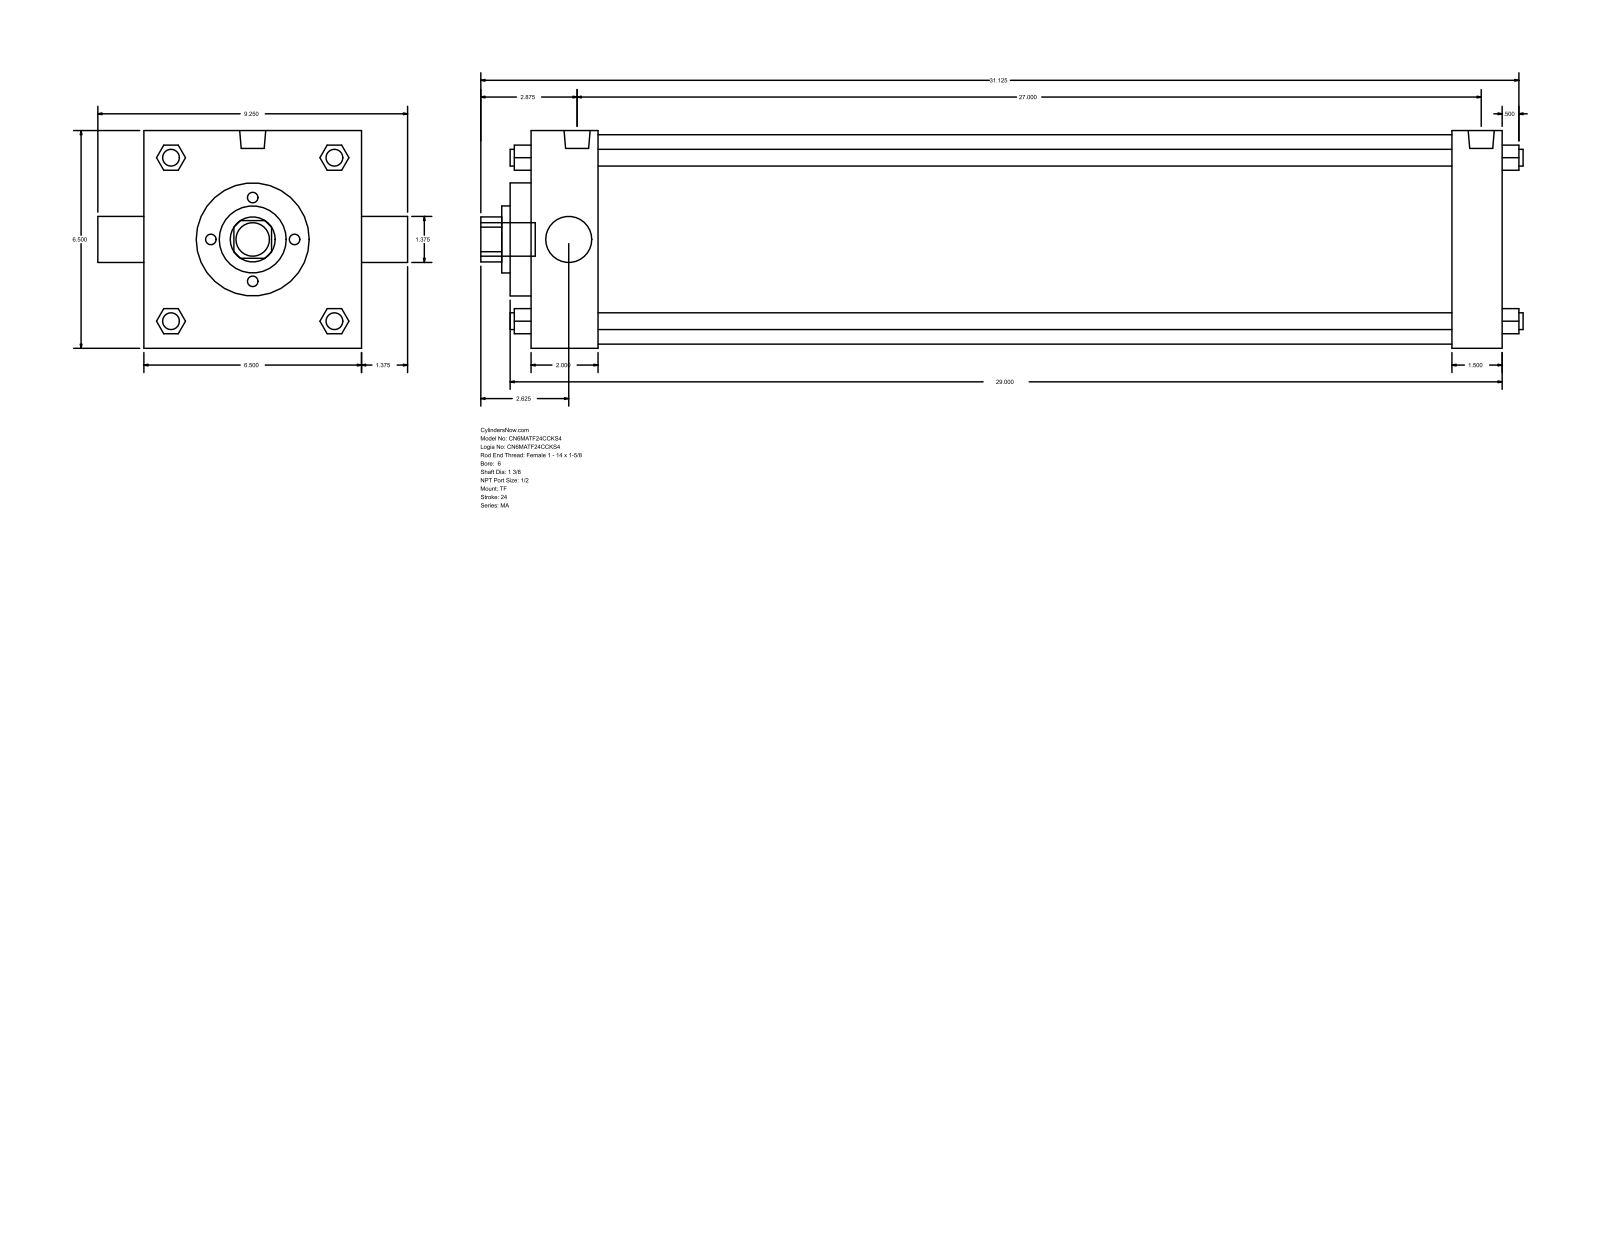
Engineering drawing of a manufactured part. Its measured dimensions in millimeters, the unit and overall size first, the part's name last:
Units: millimetres
Overall size (bounding box): 790.58 × 234.95 × 165.1
Round holes (diameter × count): ⌀34.92 ×2, ⌀50.8 ×1, ⌀85.72 ×1, ⌀158.75 ×1
Round bosses / shafts (diameter × count): ⌀12.7 ×4, ⌀17.46 ×3, ⌀19.77 ×2, ⌀25.4 ×1
Partial cylindrical surfaces — rounded edges, fillets, slot ends (radius × count): R17.06 ×1
Main face-to-face distances: 165.1, 739.78, 50.8, 688.98, 701.67, 650.87, 38.11, 15.87, 66.67, 717.54
Bodies: 0 solids, 122 faces (93 planar, 29 cylindrical, 0 other)
Part name (STEP PRODUCT): MA_TF__0600_1.375
STEP written by: GSSL Pune (CONFIG_CONTROL_DESIGN)
